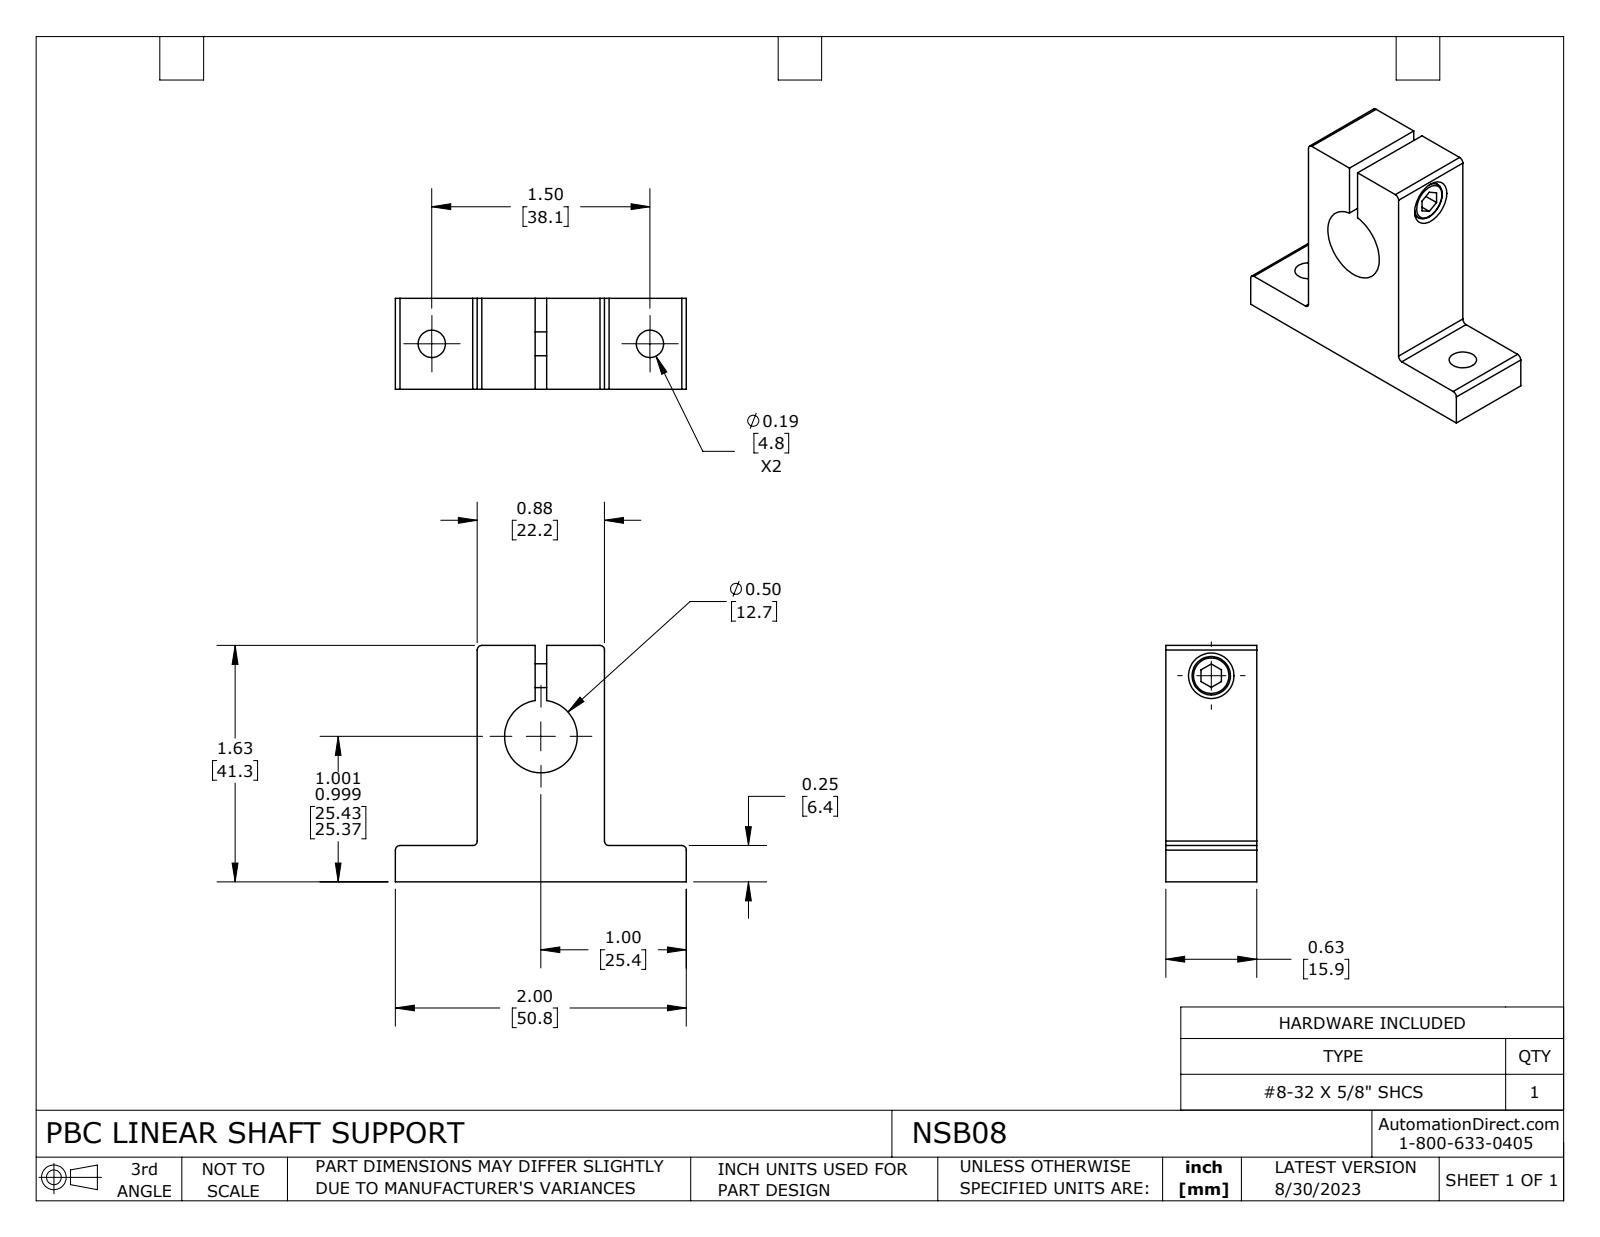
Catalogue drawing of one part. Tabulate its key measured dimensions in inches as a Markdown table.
| quantity | value |
| --- | --- |
| part name | NSB08 |
| STEP written by | SolidWorks 2023 (CONFIG_CONTROL_DESIGN) |
| units | inches |
| bodies | 2 solids, 51 faces (24 planar, 23 cylindrical, 4 other) |
| overall size | 2 × 1.625 × 0.625 |
| volume | 0.903 in³ |
| surface area | 9.986 in² |
| round holes (diameter × count) | 0.188 × 2, 0.136 × 1, 0.204 × 1, 0.313 × 1, 0.5 × 1 |
| round bosses / shafts (diameter × count) | 0.264 × 1, 0.164 × 1 |
| partial cylindrical surfaces (radius × count) | 0.031 × 6 |
| main face-to-face distances | 0.625, 0.875, 0.25, 1.625, 1.375, 0.398, 0.477, 0.563, 0.961, 1.039 |
| hole center spacings | 1.5 |
